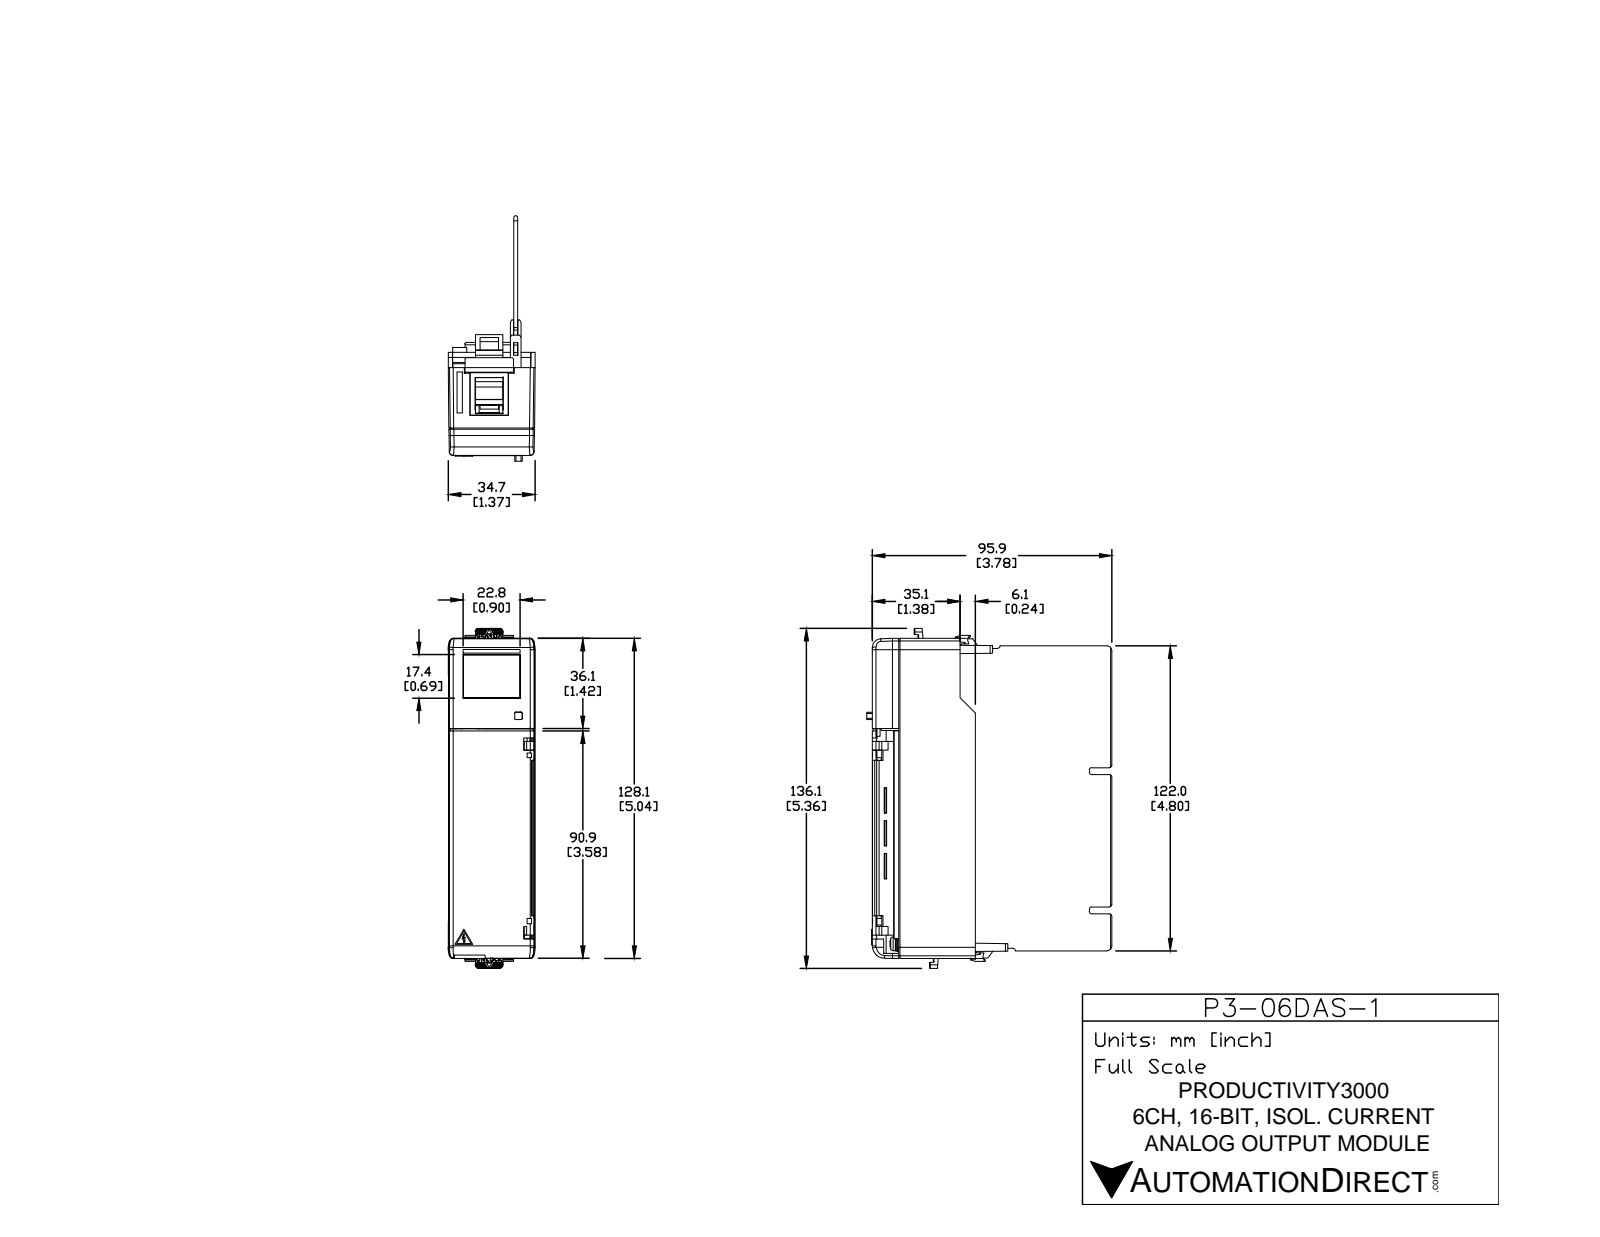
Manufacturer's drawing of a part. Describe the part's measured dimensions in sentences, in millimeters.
The part is named "P3-06DAS-1". Its 3-D file was written by "SolidWorks 2009 (CONFIG_CONTROL_DESIGN)". It is 1 solid with 3823 faces: 2833 planar, 744 cylindrical and 246 other. Overall it measures 136.08 by 98.18 by 34.8 millimeters. Its volume is 101 360 cubic millimeters and its surface area 75 361 square millimeters. Round holes: 22 of diameter 3.2, 2 of diameter 5, 1 of diameter 1.8. Round bosses or shafts: 22 of diameter 5.5, 22 of diameter 3, 20 of diameter 2.4, 2 of diameter 5.6, 2 of diameter 2.2, 2 of diameter 2, 1 of diameter 1.5. Partial cylindrical surfaces (rounded edges, fillets, slot ends): 95 of radius 0.5, 33 of radius 1, 29 of radius 0.3, 22 of radius 1.67, 13 of radius 1.5, 6 of radius 2, 5 of radius 0.2, 4 of radius 0.1. The main face-to-face distances are 1.6, 1.7, 28.23, 26.53, 32.56, 22.2, 2.2, 7.9, 6.8, 5.32. The hole center spacings are 8.68, 7.62, 13.84, 15.24, 20.59, 22.86, 27.79, 30.48.
